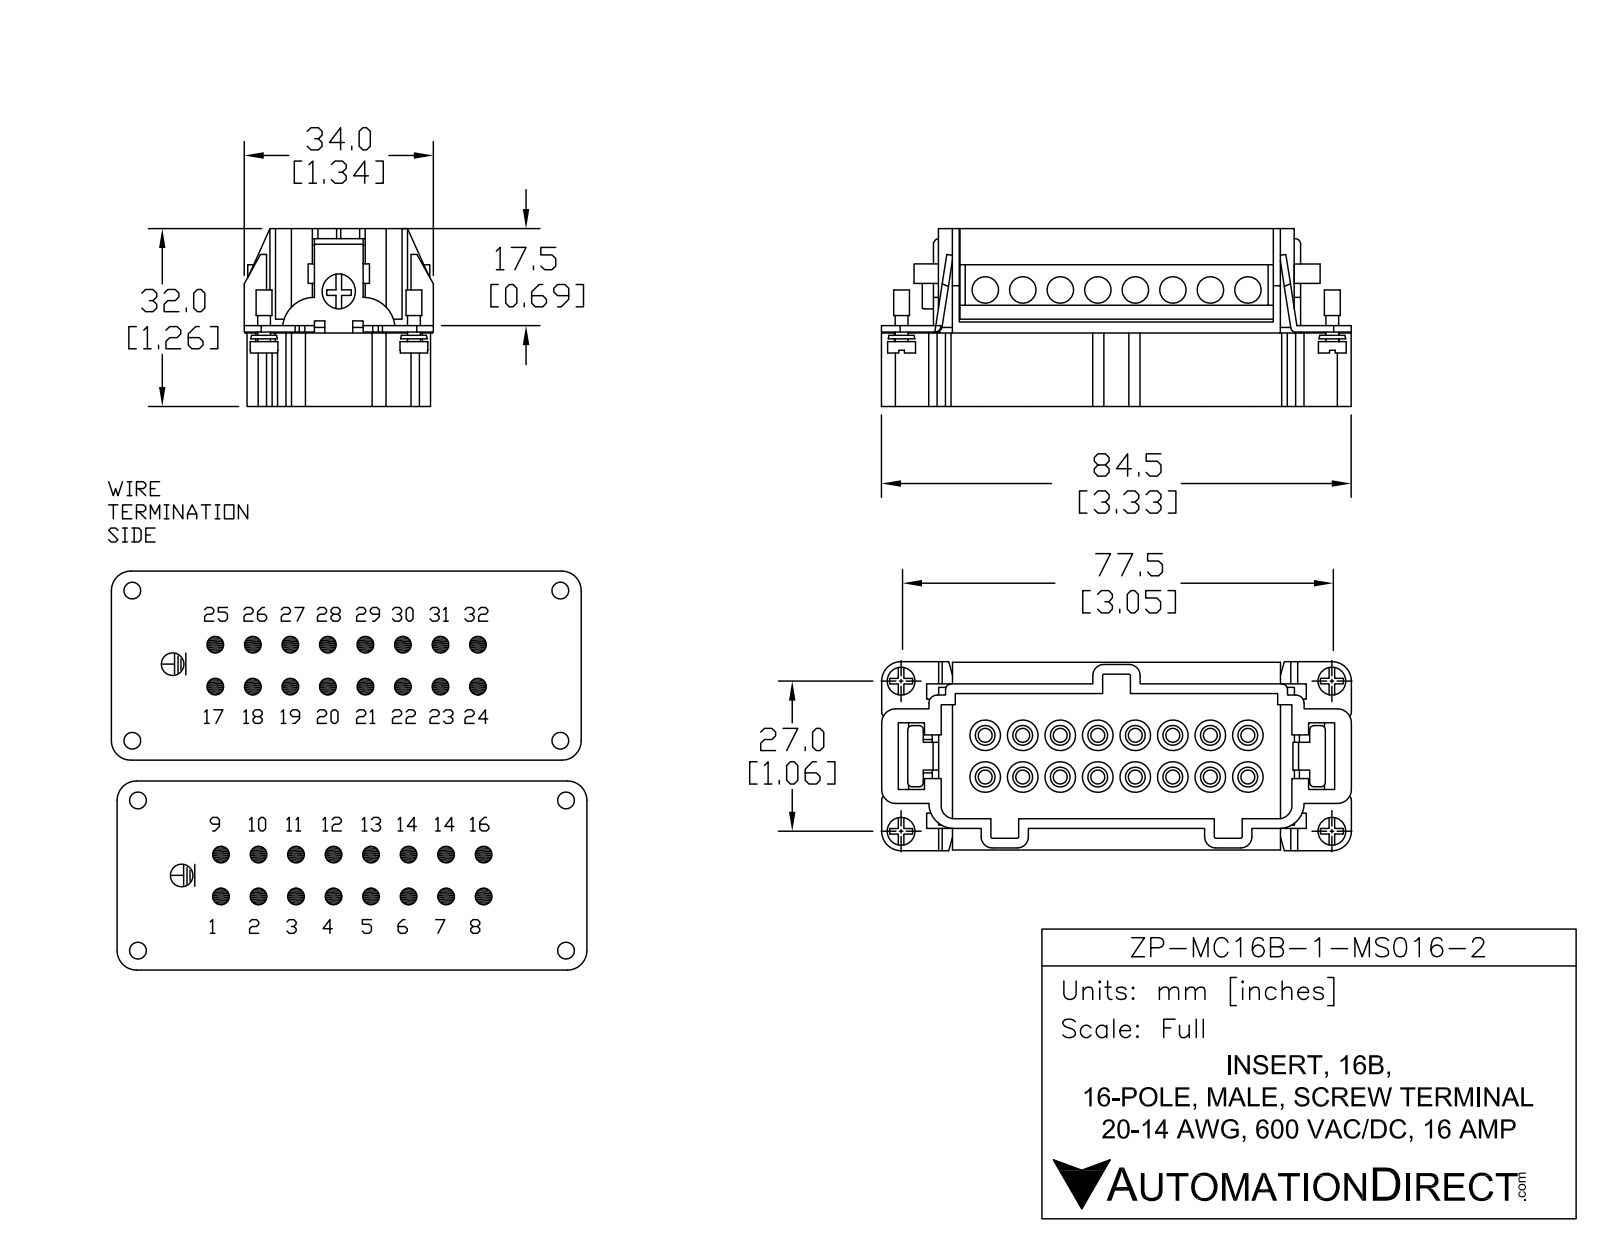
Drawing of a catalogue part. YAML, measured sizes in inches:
part_name: "ZP-MC16B-1-MS016-2"
step_written_by: "SolidWorks 2021 (CONFIG_CONTROL_DESIGN)"
units: inches
bodies: {solids: 1, faces: 2778, planar: 1329, cylindrical: 755, other: 694}
overall_size: [3.346, 1.331, 1.291]
volume: 2.18
surface_area: 50.29
round_holes:
  - {diameter: 0.126, count: 17}
  - {diameter: 0.106, count: 12}
  - {diameter: 0.067, count: 8}
round_bosses_or_shafts:
  - {diameter: 0.157, count: 17}
  - {diameter: 0.098, count: 16}
  - {diameter: 0.213, count: 4}
  - {diameter: 0.205, count: 4}
  - {diameter: 0.118, count: 4}
  - {diameter: 0.091, count: 4}
  - {diameter: 0.276, count: 1}
  - {diameter: 0.197, count: 1}
partial_cylinders:
  - {radius: 0.012, count: 102}
  - {radius: 0.008, count: 76}
  - {radius: 0.02, count: 53}
  - {radius: 0.039, count: 52}
  - {radius: 0.022, count: 24}
  - {radius: 0.089, count: 16}
  - {radius: 0.079, count: 14}
  - {radius: 0.03, count: 8}
face_to_face_distances: [0.047, 0.261, 0.626, 0.11, 0.282, 0.589, 0.098, 0.522, 0.368, 0.086]
hole_center_spacings: [0.264, 0.528, 0.791, 0.396, 0.605, 1.055, 0.844, 1.319]
